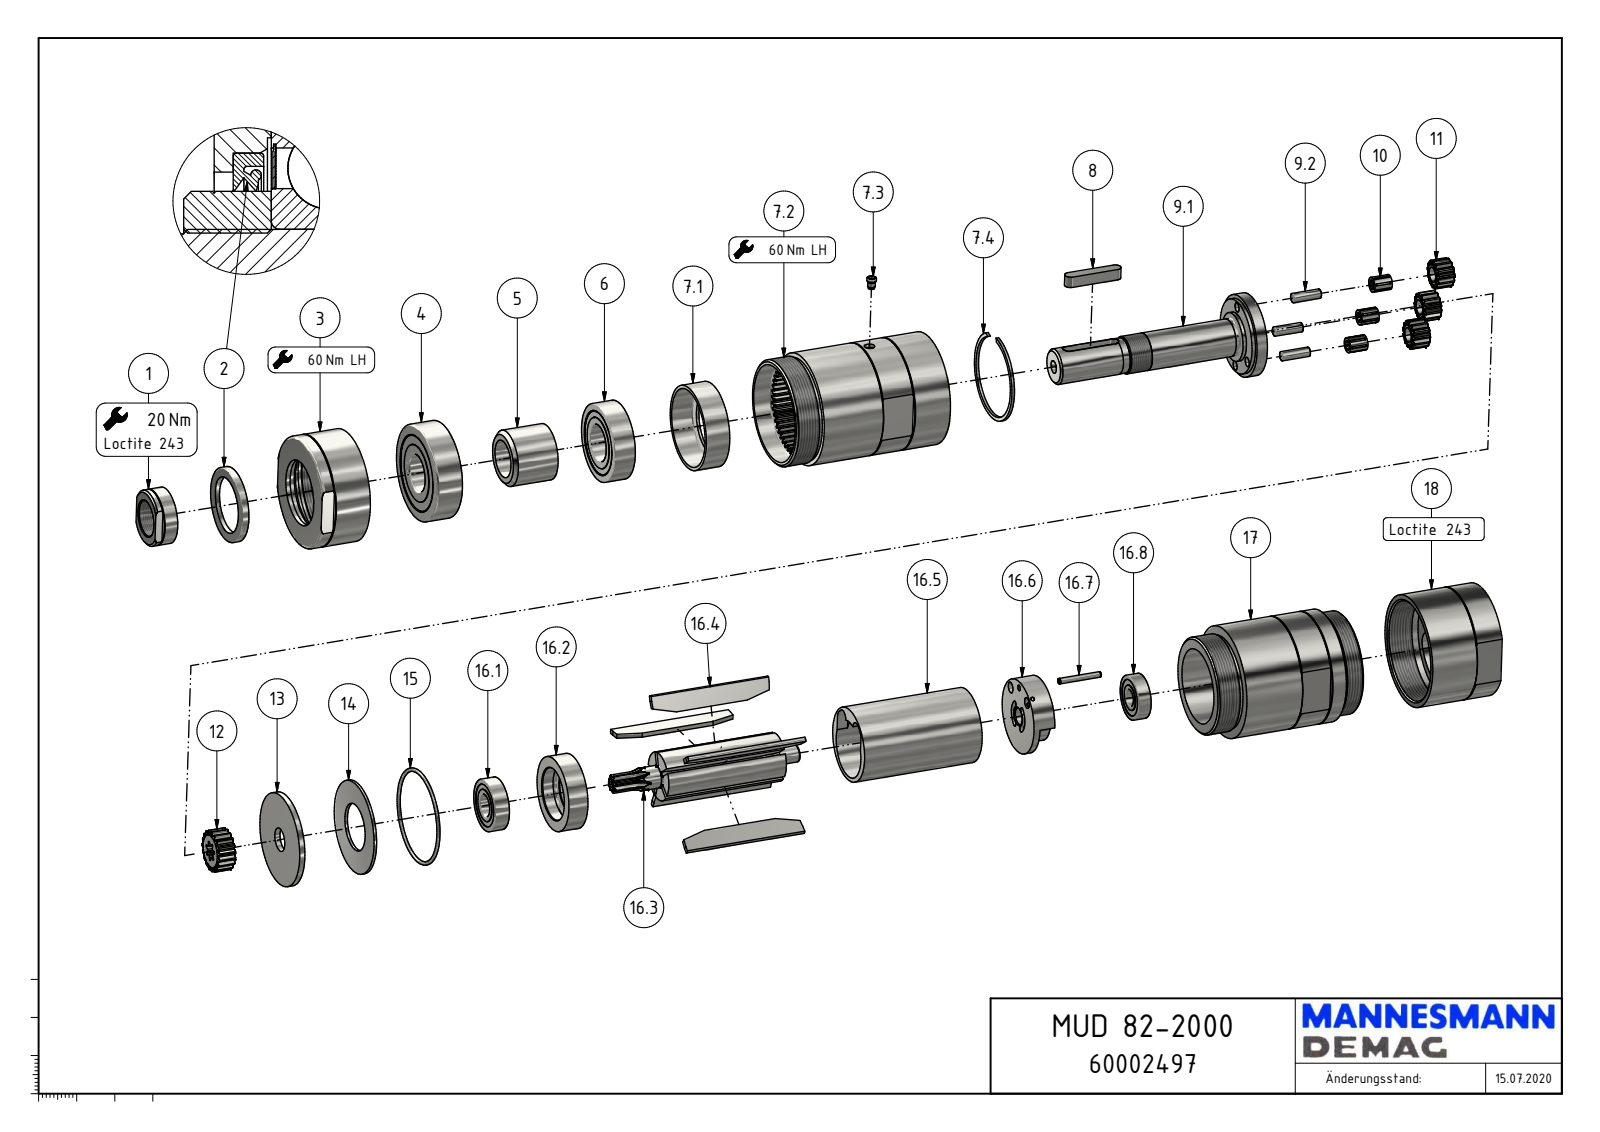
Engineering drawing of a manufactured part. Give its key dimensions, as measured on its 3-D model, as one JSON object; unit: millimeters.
{"part_name": "MUD 82-2000_60002497", "step_written_by": "Autodesk Inventor 2018 (AUTOMOTIVE_DESIGN)", "units": "millimeters", "bodies": {"solids": 1, "faces": 197, "planar": 108, "cylindrical": 44, "other": 45}, "overall_size": [243, 60, 60], "volume_mm3": 557825, "surface_area_mm2": 52656, "round_holes": [[14.95, 2], [1.55, 1], [4, 1], [4.13, 1], [5.5, 1], [18.63, 1], [35, 1], [55.38, 1]], "round_bosses_or_shafts": [[60, 1], [55.18, 1], [29.95, 1], [19, 1], [18.8, 1], [5, 1], [3.6, 1]], "partial_cylinders_radius": [[3, 2], [7.5, 2], [8.5, 1], [19.09, 1], [23.5, 1], [25.65, 1]], "face_to_face_distances": [199, 55, 182.74, 16.26, 186, 3.26, 13, 158.5, 27.5, 155.24], "hole_center_spacings": [17.41, 30.19, 16, 27]}
